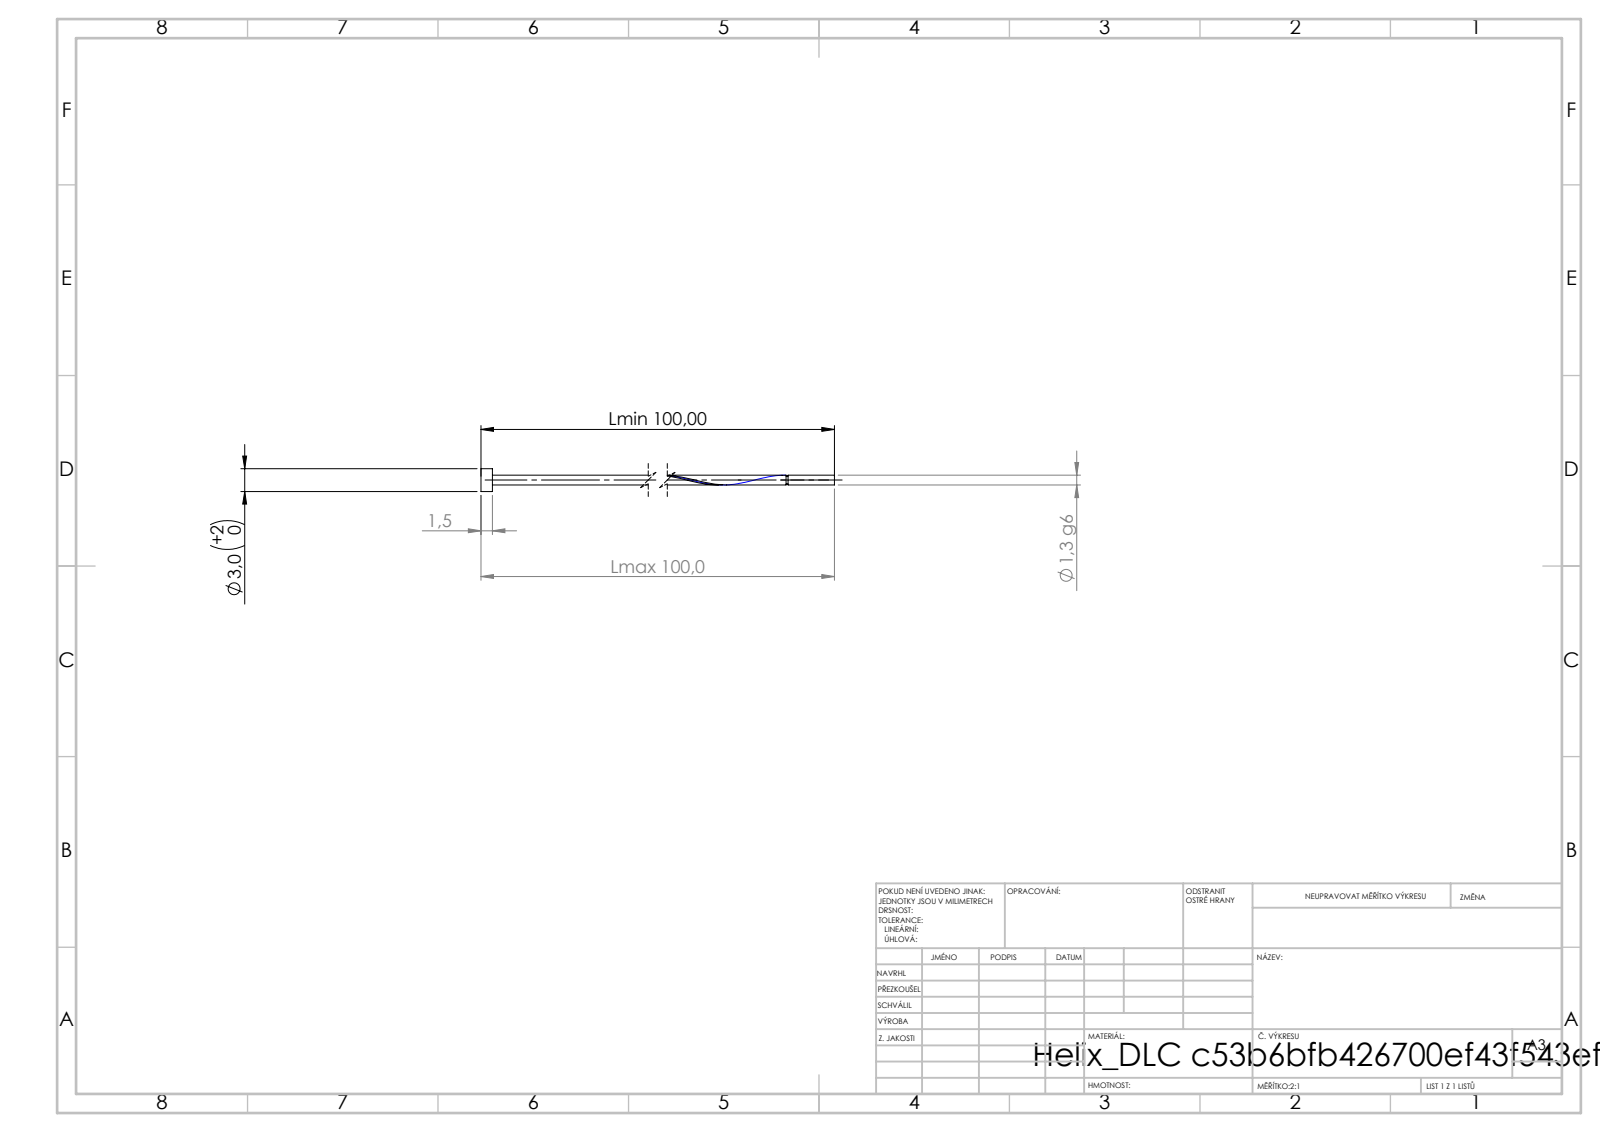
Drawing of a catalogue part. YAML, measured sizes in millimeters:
step_written_by: "SolidWorks 2019 (CONFIG_CONTROL_DESIGN)"
units: millimeters
bodies: {solids: 1, faces: 16, planar: 6, cylindrical: 9, other: 1}
overall_size: [100, 3, 3]
volume: 169
surface_area: 574
round_bosses_or_shafts:
  - {diameter: 3, count: 1}
  - {diameter: 1.3, count: 1}
  - {diameter: 1.04, count: 1}
face_to_face_distances: [1.5, 100, 98.5, 93.91, 92.41, 6.09, 93.65, 92.15, 6.35, 43.65]
